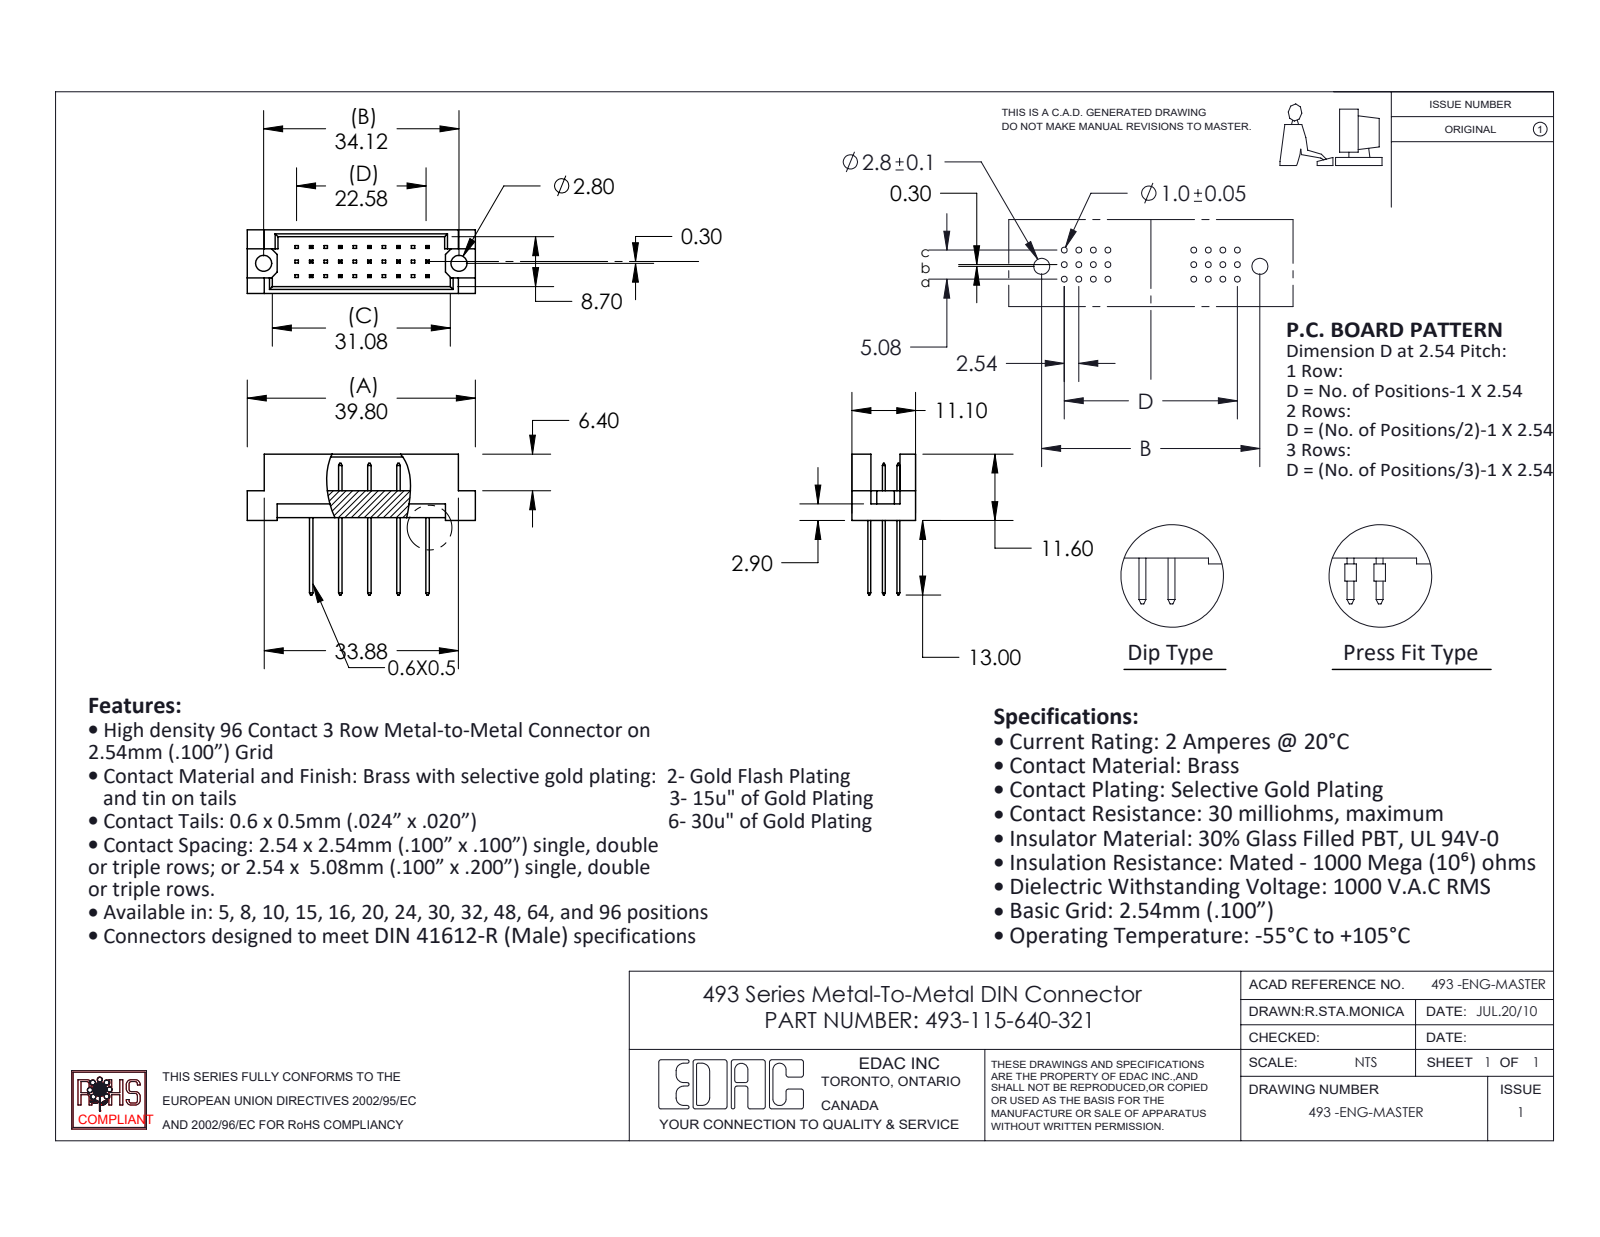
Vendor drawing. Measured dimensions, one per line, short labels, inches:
name: 493-115-640-321; 493 Part_30; 493-290_40
written by: SolidWorks 2020 (CONFIG_CONTROL_DESIGN)
unit: in
bodies: 16 solids, 382 faces (378 planar, 4 cylindrical, 0 other)
size: 1.567 × 0.969 × 0.437
volume: 0.151 in³; area: 5.411 in²
holes: 2× ⌀0.11
face distances: 0.2, 0.047, 0.39, 0.437, 0.02, 0.1, 0.343, 0.185, 0.4, 0.024
hole spacings: 1.343
